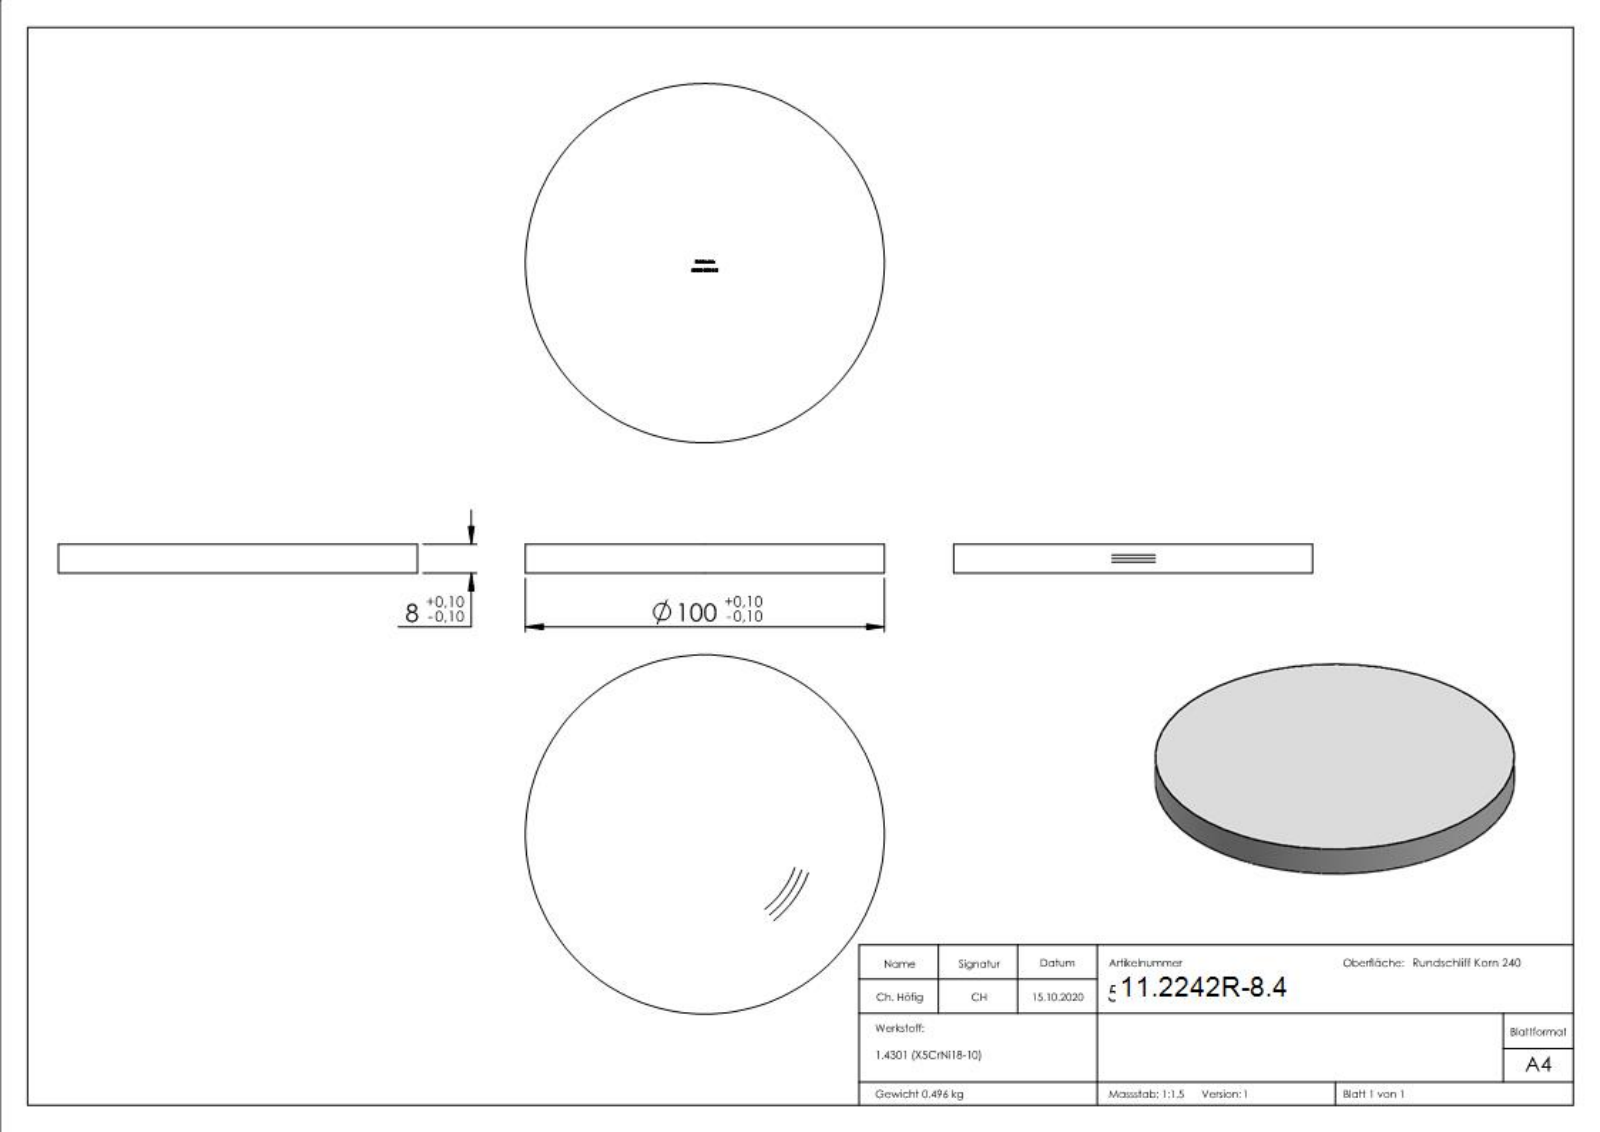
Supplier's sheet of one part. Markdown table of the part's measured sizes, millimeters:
| quantity | value |
| --- | --- |
| part name | 53100-240-8-R |
| STEP written by | SolidWorks 2018 (CONFIG_CONTROL_DESIGN) |
| units | millimeters |
| bodies | 1 solid, 271 faces (144 planar, 2 cylindrical, 125 other) |
| overall size | 100 × 100 × 8 |
| volume | 62 832 mm³ |
| surface area | 18 228 mm² |
| round bosses / shafts (diameter × count) | 100 × 1 |
| main face-to-face distances | 8, 7.9, 0.71, 1.78, 0.53, 0.83, 0.45, 2.77, 1.88, 2.45 |
